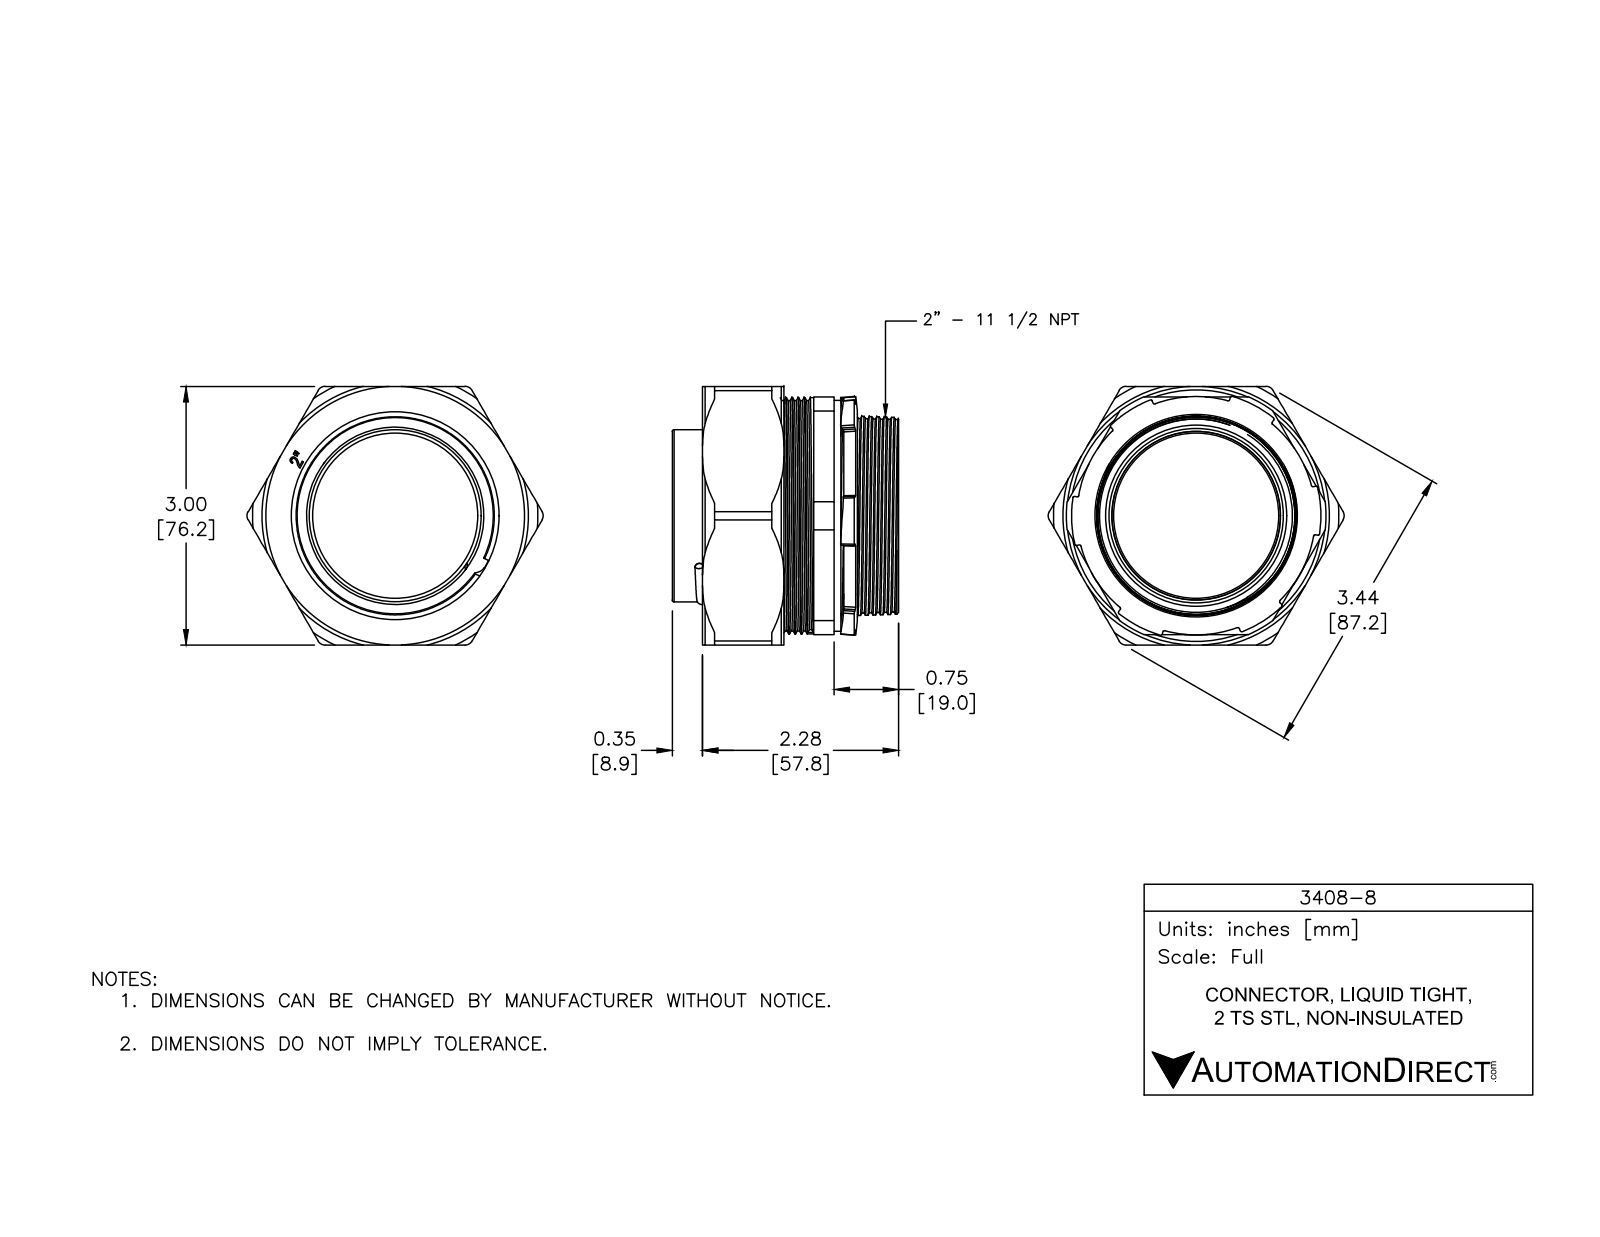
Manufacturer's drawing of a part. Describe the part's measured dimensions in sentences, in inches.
The part is named "3408 SEAL_2; 3408 COMPRESSION NUT HEX_2; 3408 FERRULE_installed; 3408 STRAIGHT BODY (+3 more)". Its 3-D file was written by "SolidWorks 2014 (AUTOMOTIVE_DESIGN)". It is 6 solids with 512 faces: 196 planar, 119 cylindrical and 197 other. Overall it measures 3.435 by 3 by 2.626 inches. Its volume is 5.151 cubic inches and its surface area 111.3 square inches. Round holes: 1 of diameter 0.222, 1 of diameter 1.915, 1 of diameter 1.957, 1 of diameter 2.024, 1 of diameter 2.268, 1 of diameter 2.362, 1 of diameter 2.402, 1 of diameter 2.409, 1 of diameter 2.472, 1 of diameter 2.701. Round bosses or shafts: 1 of diameter 2.742, 1 of diameter 2.677, 1 of diameter 2.598, 1 of diameter 2.441, 1 of diameter 1.996, 1 of diameter 1.955, 1 of diameter 0.181. Partial cylindrical surfaces (rounded edges, fillets, slot ends): 8 of radius 0.014, 6 of radius 0.094, 3 of radius 0.004, 2 of radius 0.005, 2 of radius 0.052, 1 of radius 0.007, 1 of radius 0.019, 1 of radius 0.028. The main face-to-face distances are 3, 1.527, 2.878, 0.122, 1.188, 0.339, 1.606, 0.418, 0.079, 2.756. The hole center spacings are 1.35.
